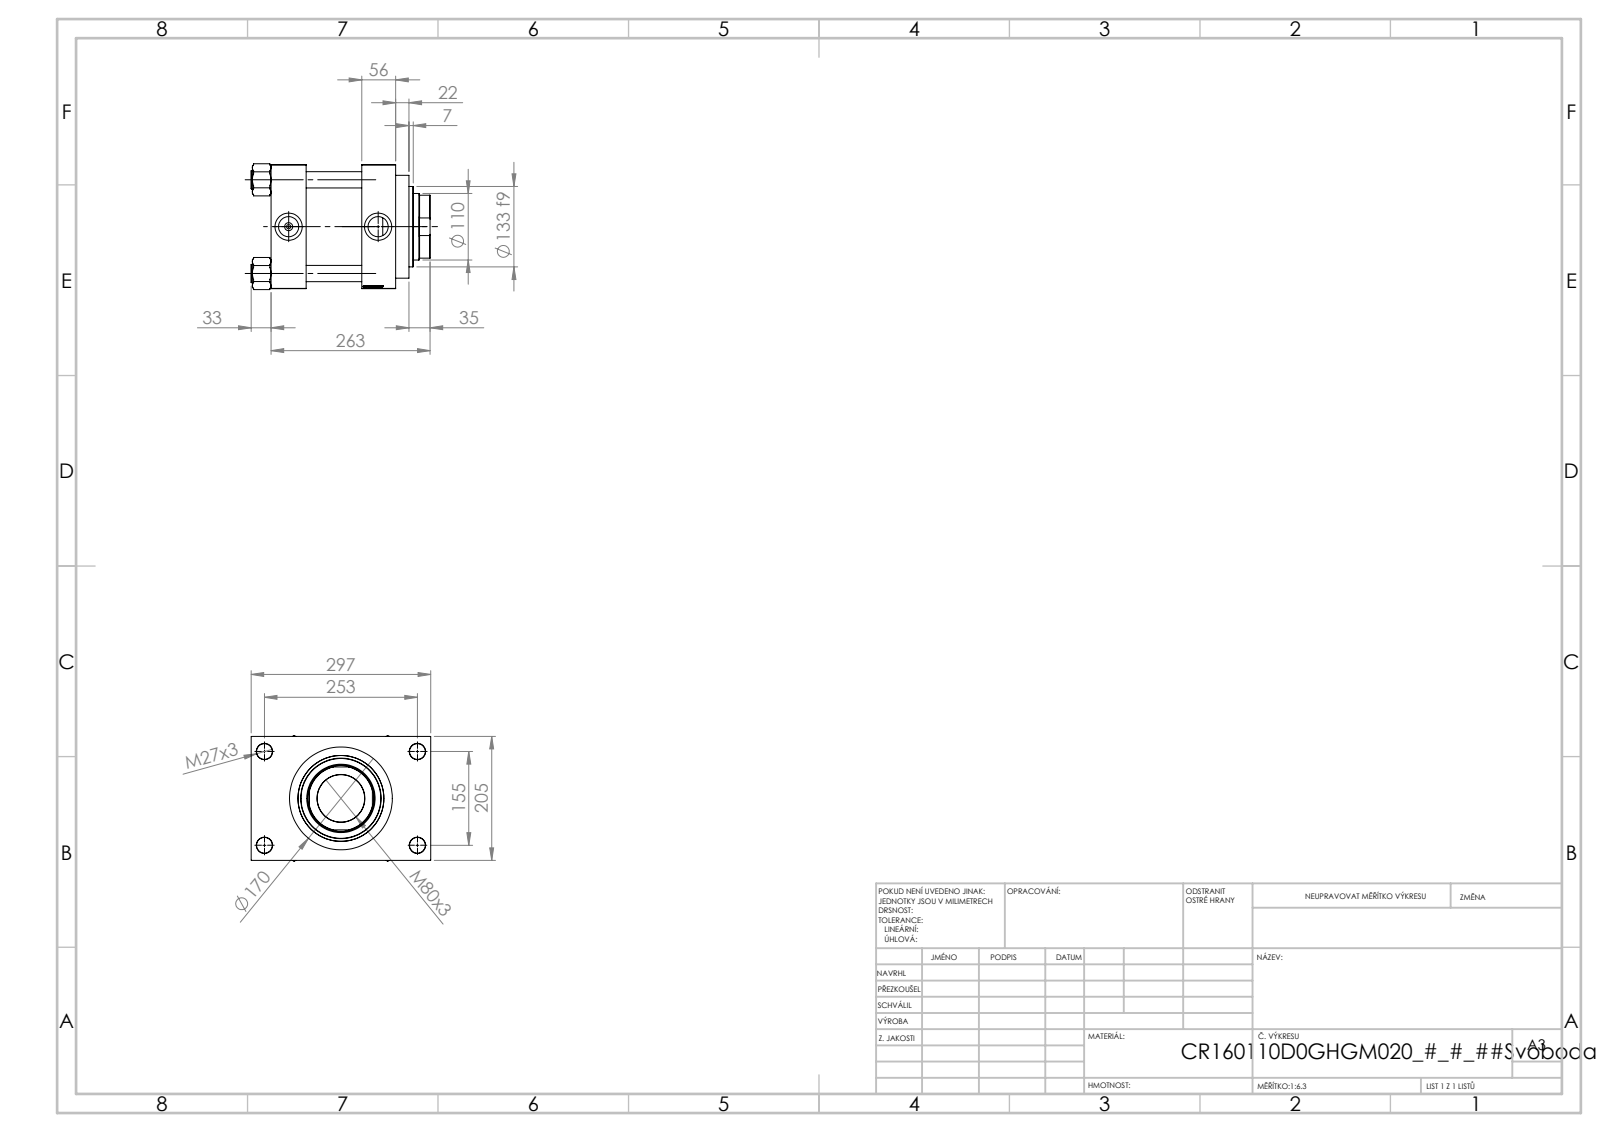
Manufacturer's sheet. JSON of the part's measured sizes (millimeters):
{"part_name": "V215CR_D_TYCINKA; V215CR_VCP_D; V215_VC_A; V215CR_D_Body (+1 more)", "step_written_by": "SolidWorks 2019 (CONFIG_CONTROL_DESIGN)", "units": "millimeters", "bodies": {"solids": 11, "faces": 1151, "planar": 545, "cylindrical": 88, "other": 518}, "overall_size": [297, 296, 208.14], "volume_mm3": 8128000, "surface_area_mm2": 779140, "round_holes": [[26, 4], [27, 4], [7, 2], [33.24, 2], [45, 2], [78.5, 1], [110, 1], [113, 1], [120, 1], [142, 1], [160, 1]], "round_bosses_or_shafts": [[30, 4], [170, 1], [166, 1], [133, 1]], "partial_cylinders_radius": [[54, 1]], "face_to_face_distances": [58, 150, 92, 205, 206, 148, 56, 46, 251, 72], "hole_center_spacings": [49.05, 109.53, 148.35, 154.9, 162.53, 203.95, 256.13, 155]}
